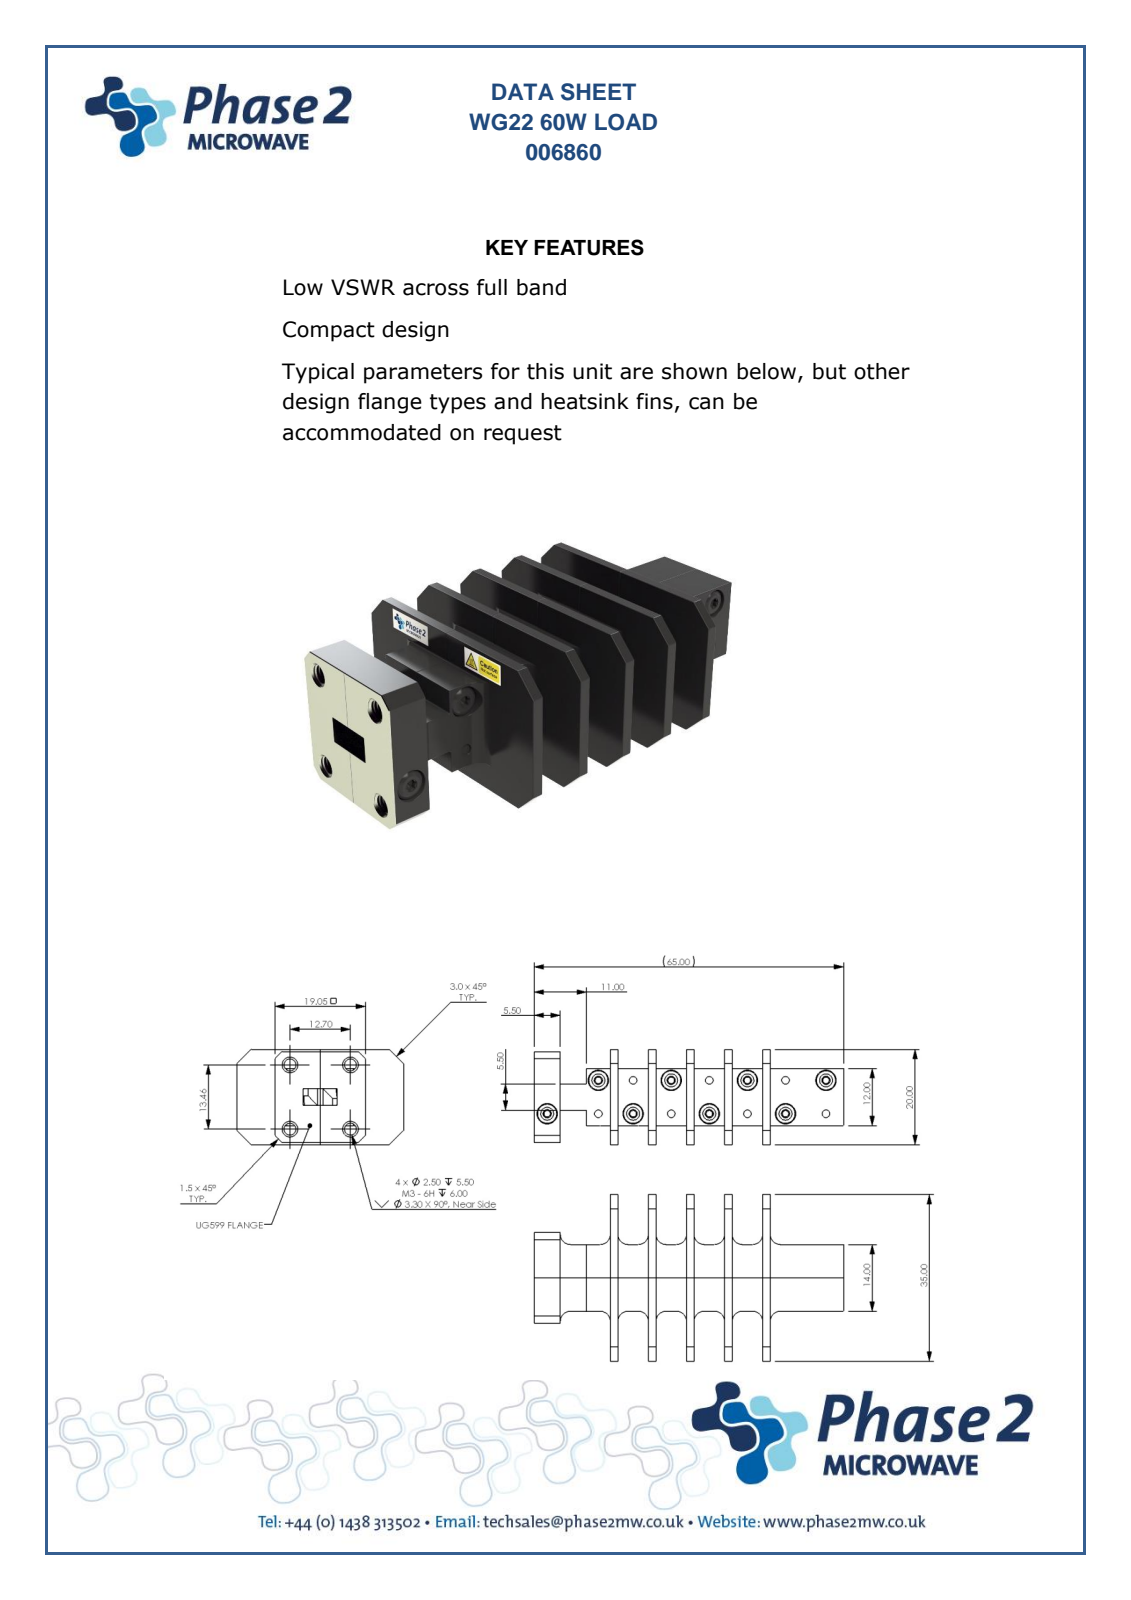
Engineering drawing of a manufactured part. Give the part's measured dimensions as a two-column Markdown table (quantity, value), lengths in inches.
| quantity | value |
| --- | --- |
| part name | 006860 |
| STEP written by | SolidWorks 2019 (CONFIG_CONTROL_DESIGN) |
| units | inches |
| bodies | 0 solids, 284 faces (170 planar, 58 cylindrical, 56 other) |
| overall size | 2.559 × 1.378 × 0.787 |
| round holes (diameter × count) | 0.069 × 8, 0.169 × 8, 0.063 × 6, 0.098 × 4 |
| partial cylindrical surfaces (radius × count) | 0.083 × 6 |
| main face-to-face distances | 0.787, 0.63, 1.323, 0.413, 0.157, 1.378, 0.217, 0.324, 0.464, 0.166 |
| hole center spacings | 0.276, 0.335, 0.423, 0.433, 0.5, 0.505, 0.53, 0.729 |
